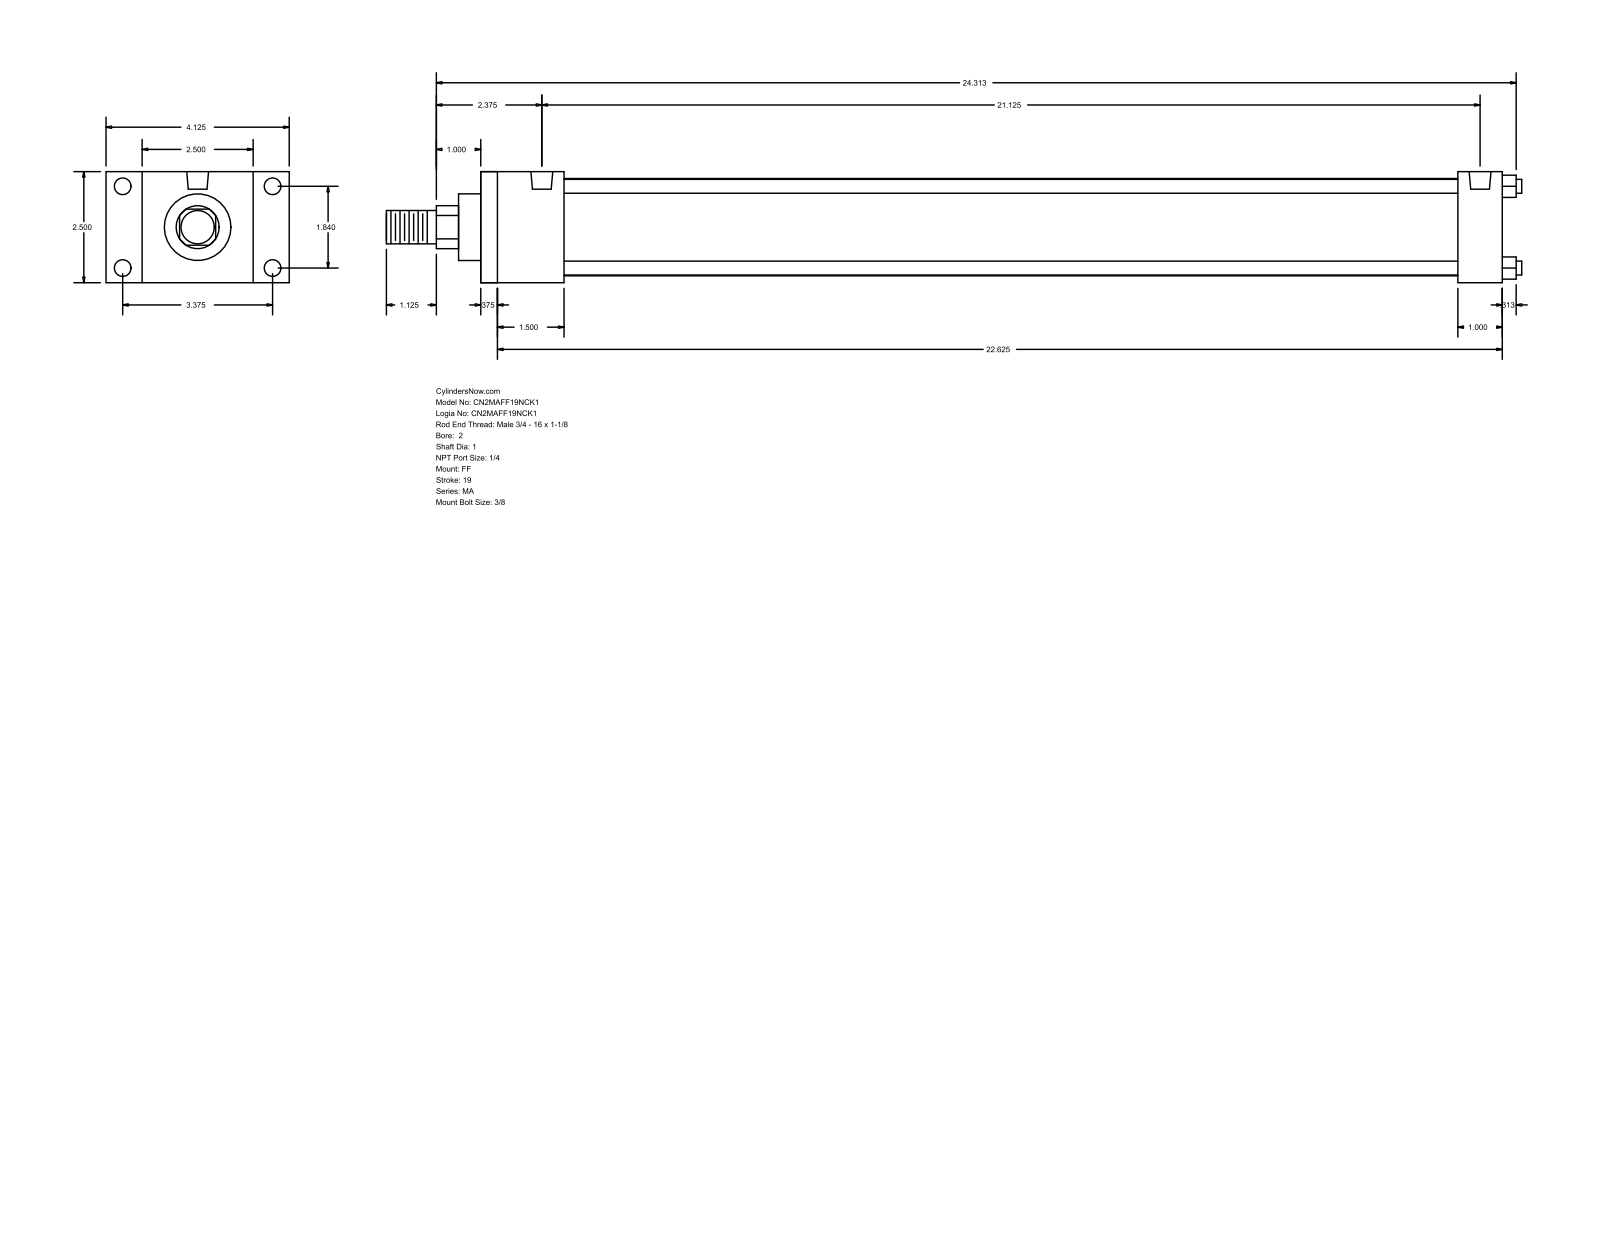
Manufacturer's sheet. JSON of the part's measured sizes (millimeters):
{"part_name": "MA_FF__0200_1", "step_written_by": "GSSL Pune (CONFIG_CONTROL_DESIGN)", "units": "millimeters", "bodies": {"solids": 0, "faces": 92, "planar": 64, "cylindrical": 28, "other": 0}, "overall_size": [649.29, 104.78, 63.5], "round_holes": [[7.94, 4], [9.53, 4], [12.49, 2]], "round_bosses_or_shafts": [[7.94, 4], [55.63, 1], [38.1, 1], [25.4, 1], [19.05, 1]], "partial_cylinders_radius": [[12.29, 1]], "face_to_face_distances": [63.5, 584.2, 9.52, 574.68, 25.4, 20.64, 12.7, 47.63, 558.8, 38.11], "hole_center_spacings": [46.74, 85.72, 97.63, 536.57]}
